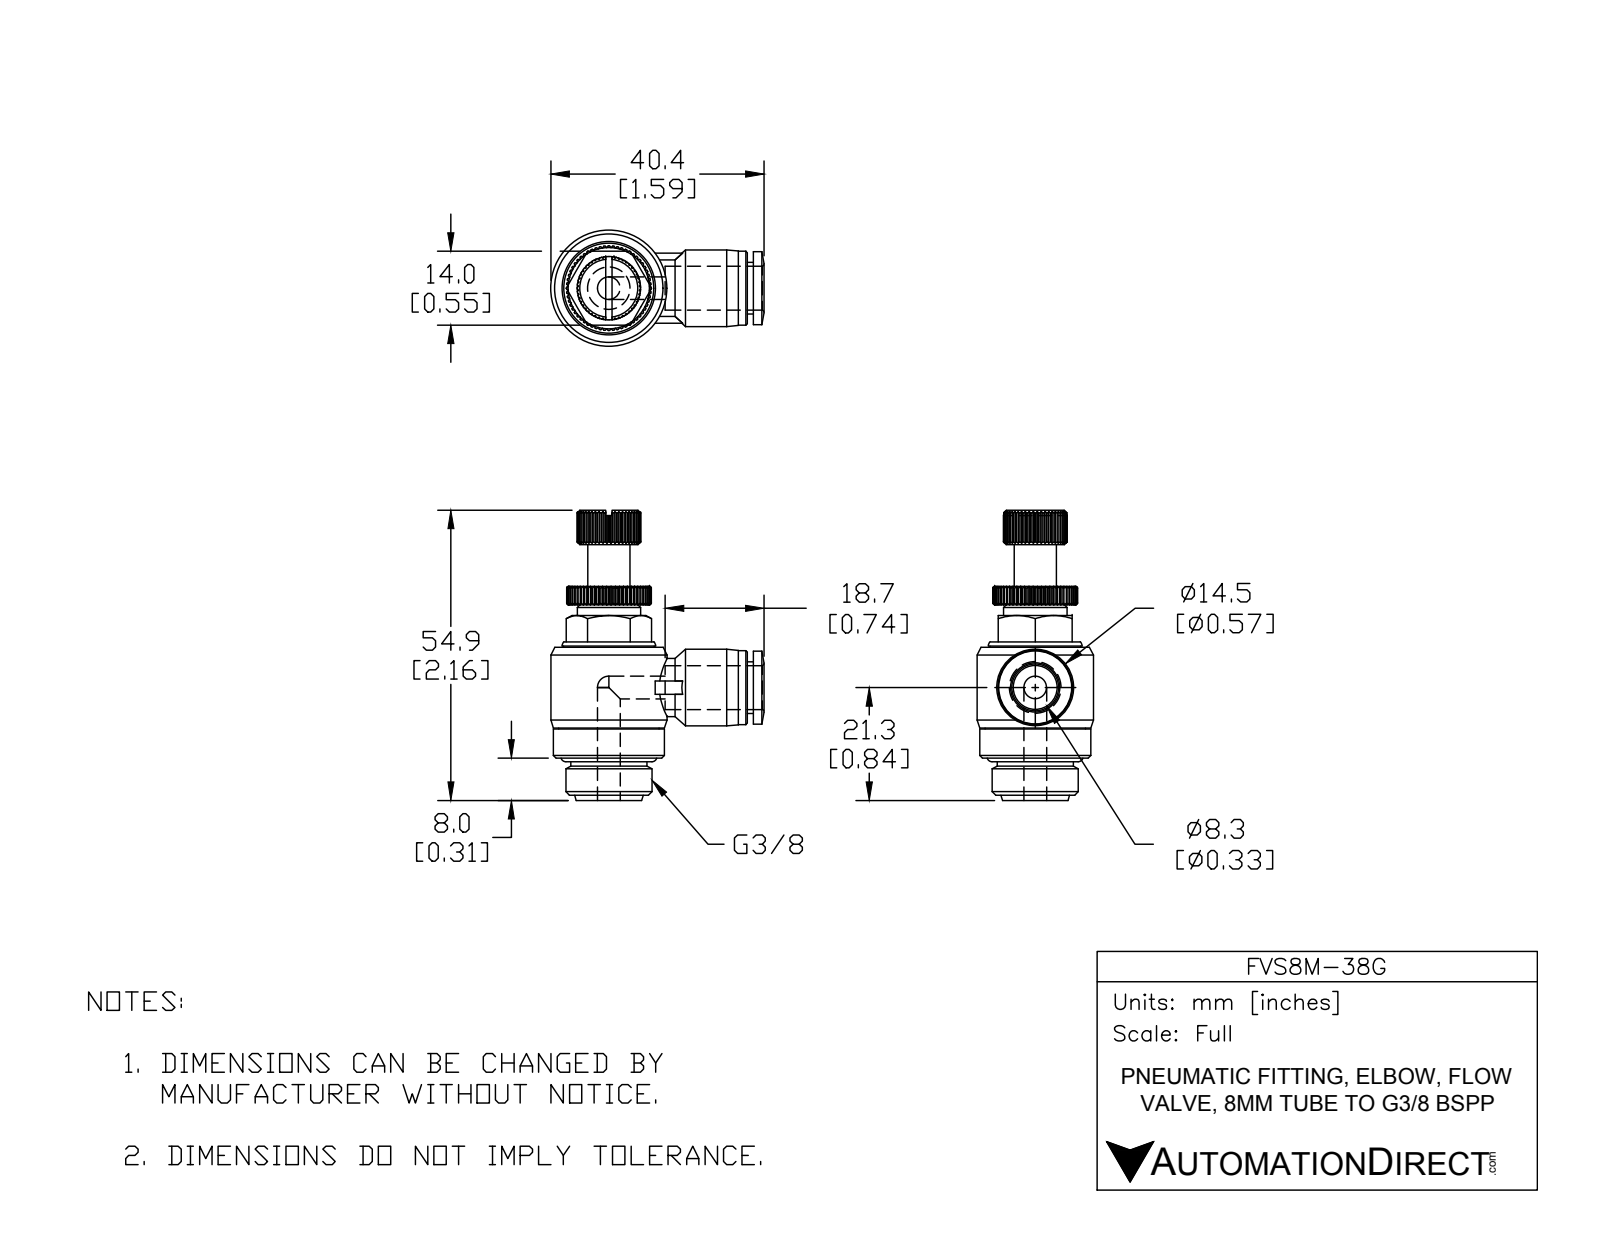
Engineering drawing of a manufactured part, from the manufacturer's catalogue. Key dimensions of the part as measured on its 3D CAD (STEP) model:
Part name (STEP PRODUCT): FVS8M-38G
STEP written by: SolidWorks 2015 (AUTOMOTIVE_DESIGN)
Units: inches
Bodies: 2 solids, 567 faces (251 planar, 143 cylindrical, 173 other)
Overall size (bounding box): 2.161 × 1.589 × 0.866
Volume: 0.828 in³ · Surface area: 9.834 in²
Round holes (diameter × count): ⌀0.169 ×2, ⌀0.327 ×1
Round bosses / shafts (diameter × count): ⌀0.866 ×1, ⌀0.827 ×1, ⌀0.748 ×1, ⌀0.675 ×1, ⌀0.642 ×1, ⌀0.571 ×1, ⌀0.567 ×1, ⌀0.551 ×1
Partial cylindrical surfaces — rounded edges, fillets, slot ends (radius × count): R0.315 ×1
Main face-to-face distances: 1.142, 0.315, 0.551, 0.039, 1.594, 1.063, 0.453, 0.276, 0.567, 0.705
